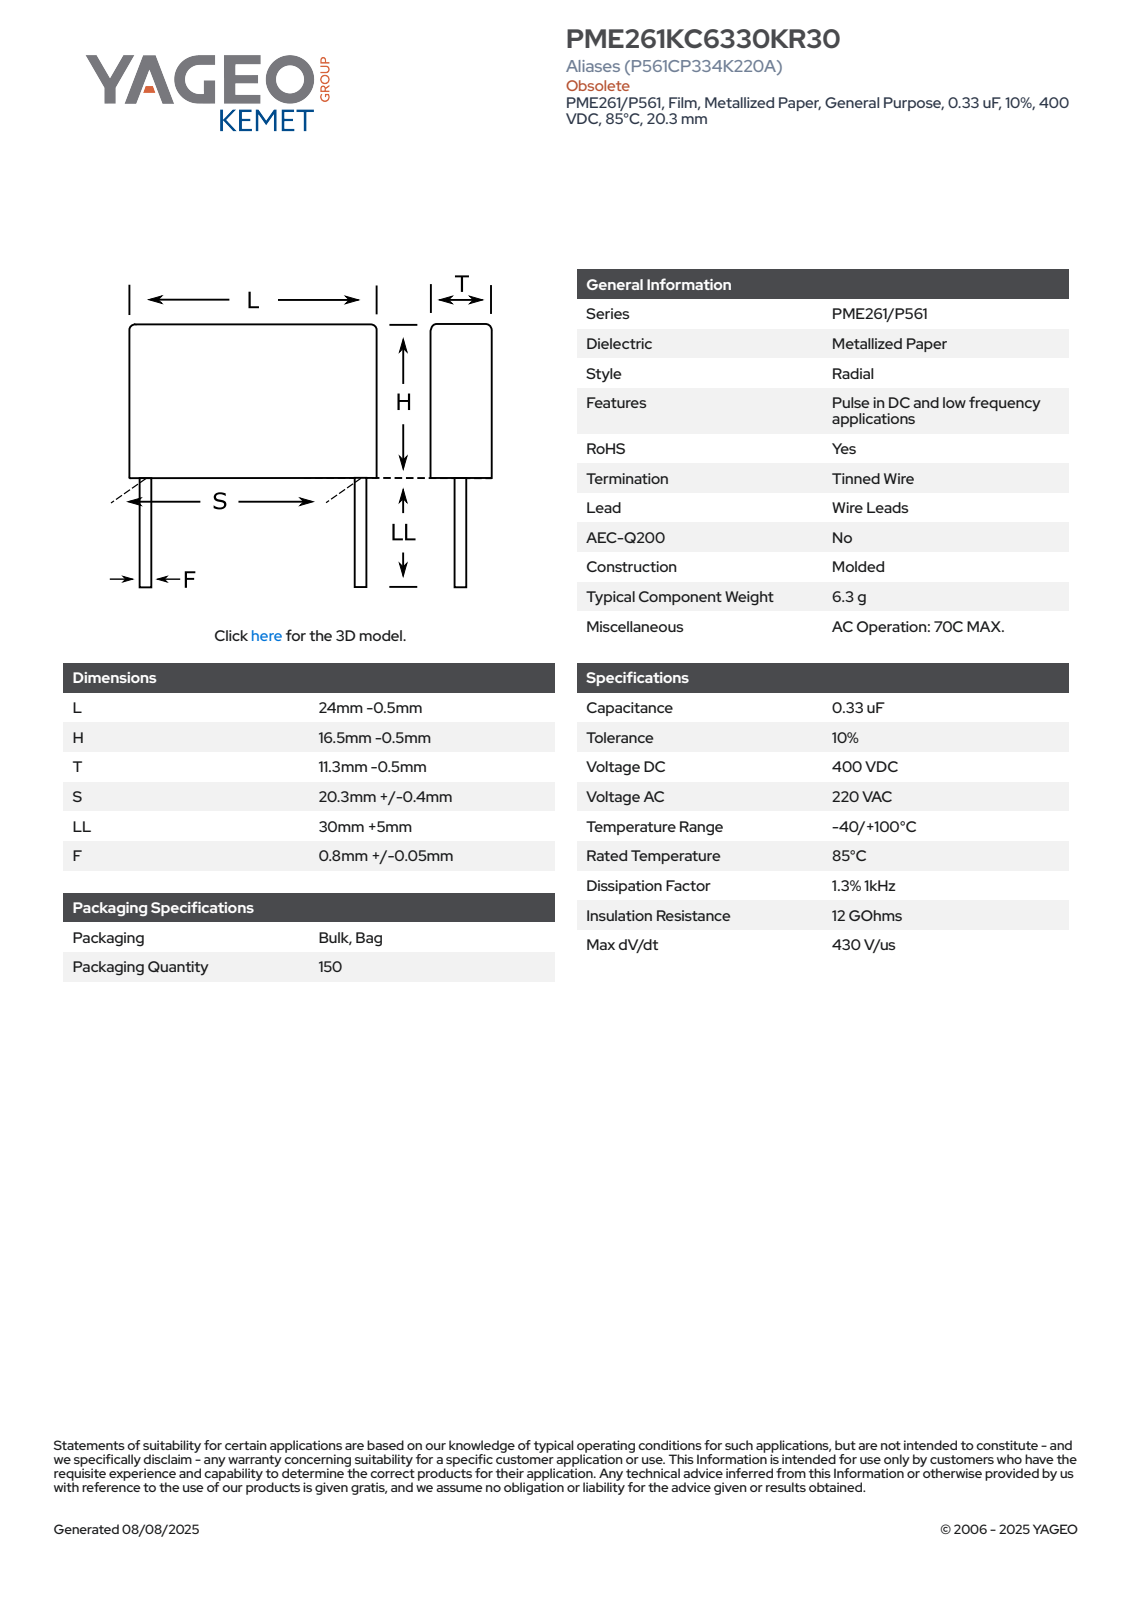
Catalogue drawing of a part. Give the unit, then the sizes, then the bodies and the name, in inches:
Units: inches
Overall size (bounding box): 2.008 × 0.925 × 0.425
Round bosses / shafts (diameter × count): ⌀0.033 ×2
Partial cylindrical surfaces — rounded edges, fillets, slot ends (radius × count): R0.02 ×4
Main face-to-face distances: 0.425, 0.63, 0.925, 1.378, 2.008, 1.725, 0.347, 0.283, 1.642, 0.264
Volume: 0.25 in³ · Surface area: 2.796 in²
Bodies: 4 solids, 73 faces (65 planar, 8 cylindrical, 0 other)
Part name (STEP PRODUCT): CFR_MOLDED_24X16.5X11.3_L23.5H16T10.8S20.3LL35F0.85
STEP written by: SolidWorks 2014 (AUTOMOTIVE_DESIGN)
